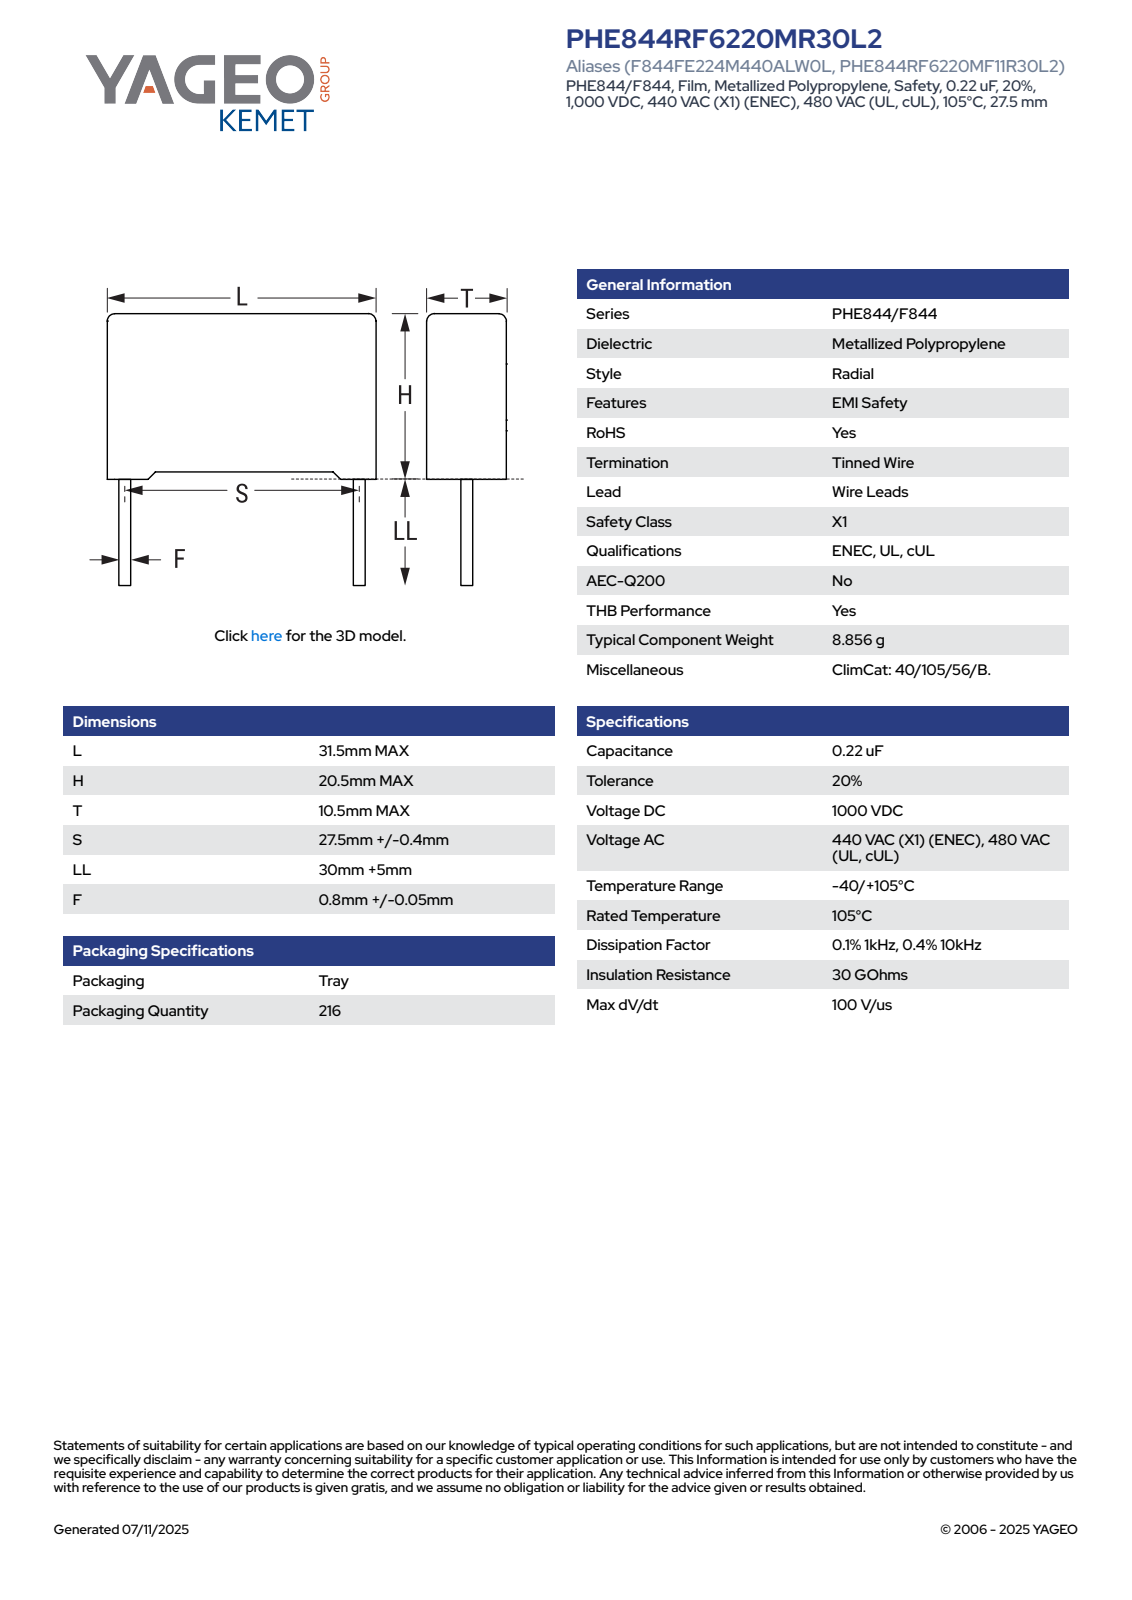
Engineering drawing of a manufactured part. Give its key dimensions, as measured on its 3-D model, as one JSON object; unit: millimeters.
{"part_name": "CFR_RB2_31.5X20.5X10.5_L31.5H20.5T10.5S27.5LL35F0.85", "step_written_by": "SolidWorks 2021 (AUTOMOTIVE_DESIGN)", "units": "millimeters", "bodies": {"solids": 4, "faces": 85, "planar": 77, "cylindrical": 8, "other": 0}, "overall_size": [55.5, 31.5, 10.51], "volume_mm3": 6596, "surface_area_mm2": 2622, "round_bosses_or_shafts": [[0.85, 2]], "partial_cylinders_radius": [[0.5, 4]], "face_to_face_distances": [10.5, 19.75, 31.5, 19.79, 0.71, 0.75, 20.5, 1.05, 10.51, 30.45]}
